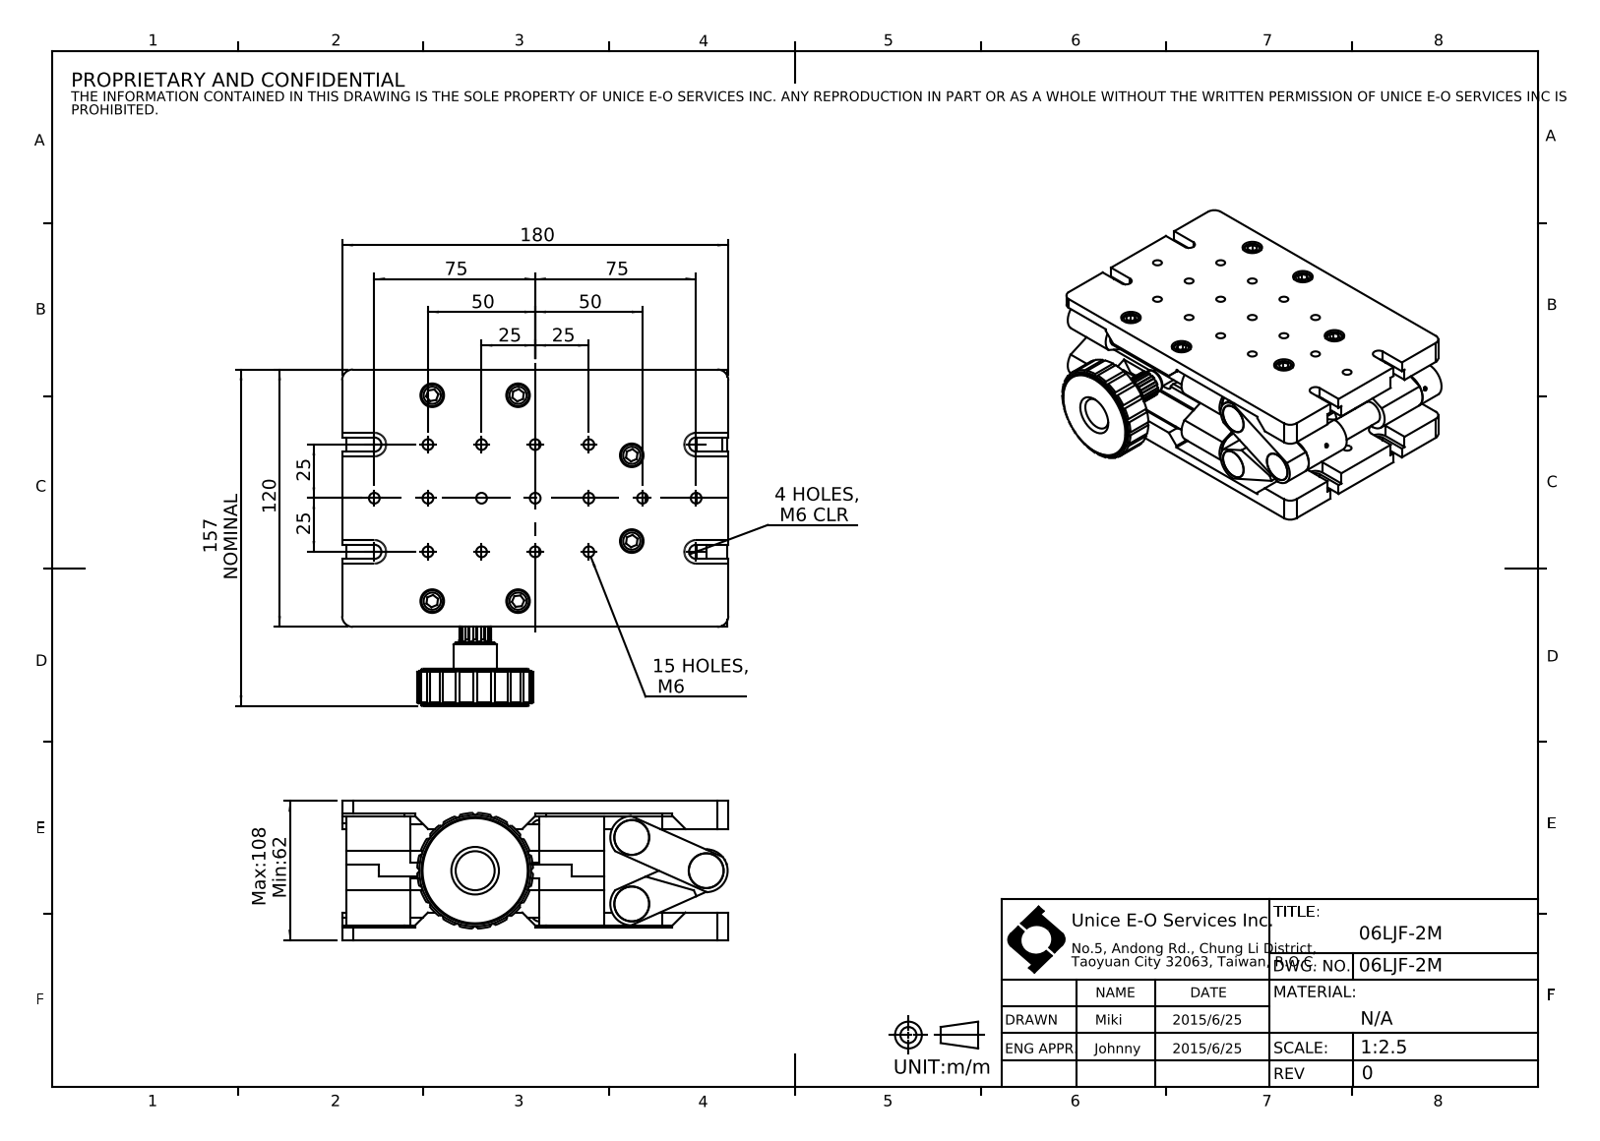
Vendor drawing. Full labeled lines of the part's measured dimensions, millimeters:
Part name (STEP PRODUCT): 06LJF-2M
STEP written by: SolidWorks 2016 (CONFIG_CONTROL_DESIGN)
Units: millimetres
Bodies: 113 solids, 1972 faces (741 planar, 797 cylindrical, 434 other)
Overall size (bounding box): 180 × 157 × 65
Volume: 887 608 mm³ · Surface area: 325 183 mm²
Round holes (diameter × count): ⌀5 ×36, ⌀6.5 ×9, ⌀12.7 ×9, ⌀16.2 ×9, ⌀2.05 ×6, ⌀6.6 ×6, ⌀11 ×6, ⌀2 ×3, ⌀3.3 ×1, ⌀6.1 ×1, ⌀8.38 ×1, ⌀8.5 ×1
Round bosses / shafts (diameter × count): ⌀6 ×16, ⌀16.3 ×9, ⌀16 ×9, ⌀10 ×7, ⌀2.5 ×6, ⌀50 ×1, ⌀20 ×1, ⌀14 ×1
Partial cylindrical surfaces — rounded edges, fillets, slot ends (radius × count): R0.3 ×24, R1 ×20, R1.5 ×12, R5 ×10, R10 ×9, R7 ×6, R3.3 ×4, R5.5 ×4
Main face-to-face distances: 13, 52, 65, 7, 6, 18, 46, 39, 59, 10.85
Hole centre spacings: 25, 55.9, 35.36, 50, 79.06, 40, 38, 75
